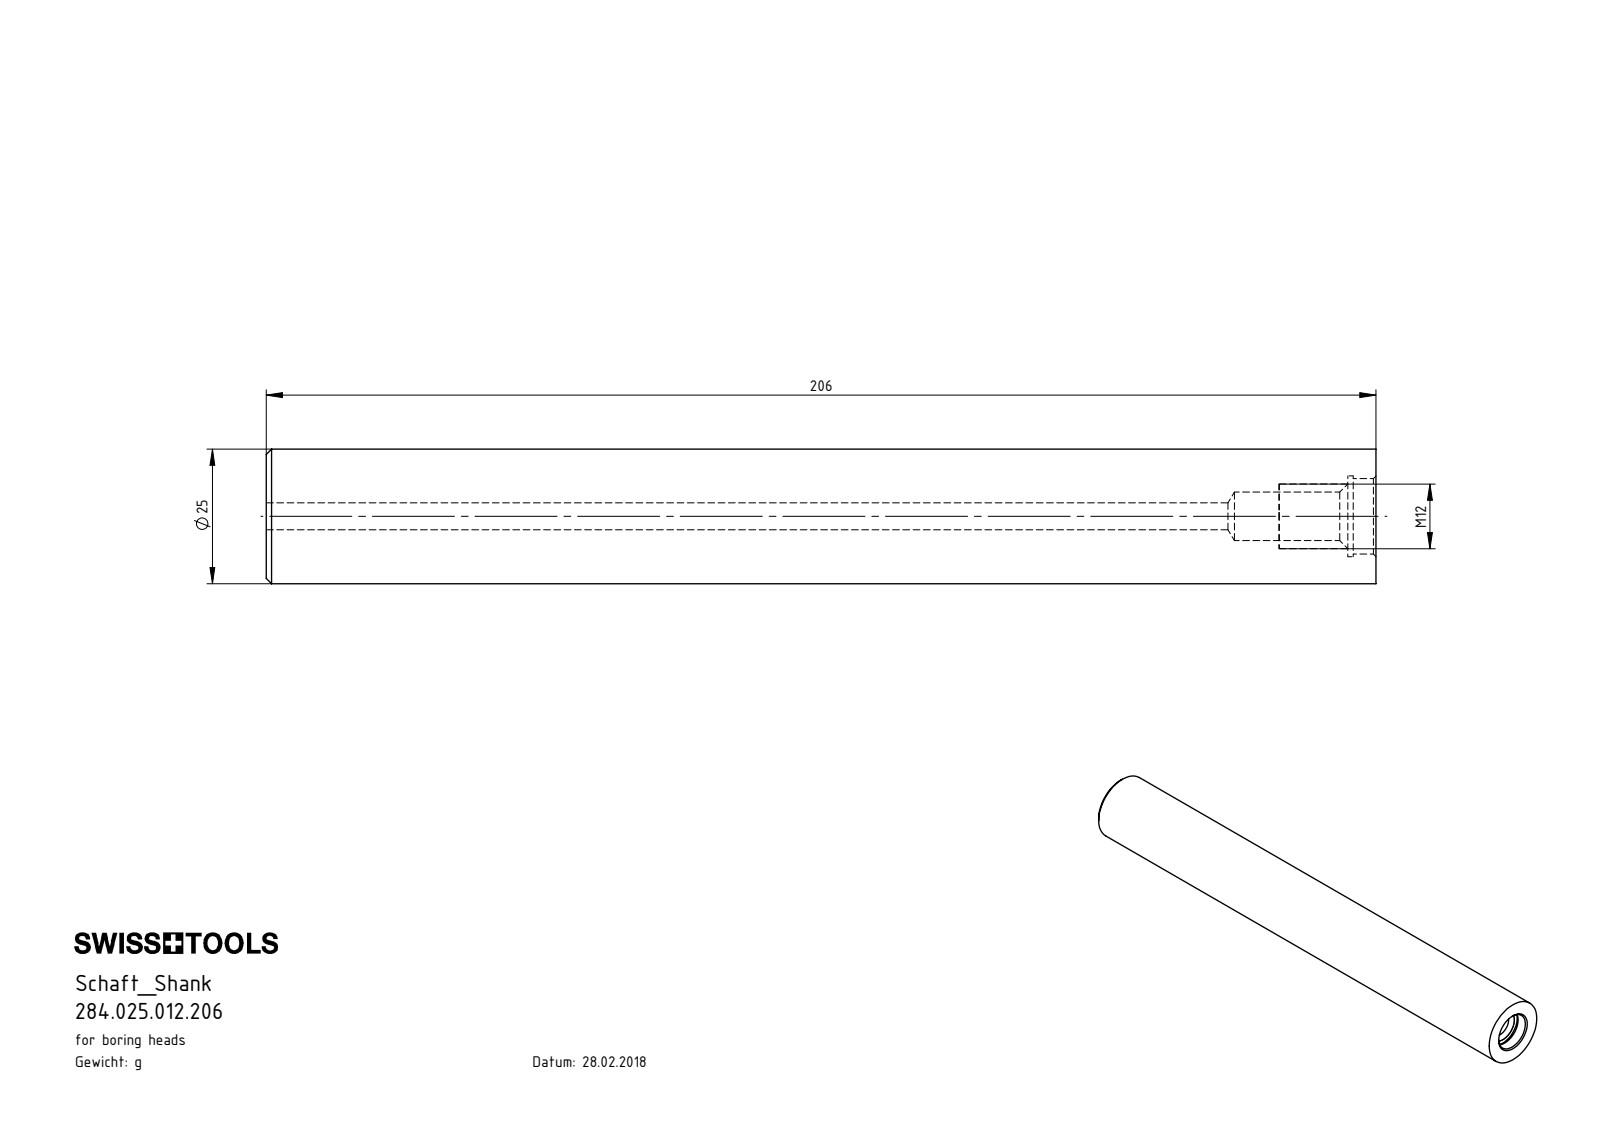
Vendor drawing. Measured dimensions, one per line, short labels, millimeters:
name: 284.025.012.206
written by: SolidWorks 2017 (CONFIG_CONTROL_DESIGN)
unit: mm
bodies: 1 solid, 22 faces (4 planar, 10 cylindrical, 8 other)
size: 206 × 25 × 25
volume: 95 318 mm³; area: 20 726 mm²
holes: 1× ⌀5, 1× ⌀9, 1× ⌀14, 1× ⌀15
bosses: 1× ⌀25
face distances: 206, 200.75, 5.25, 201.75, 1, 4.25
